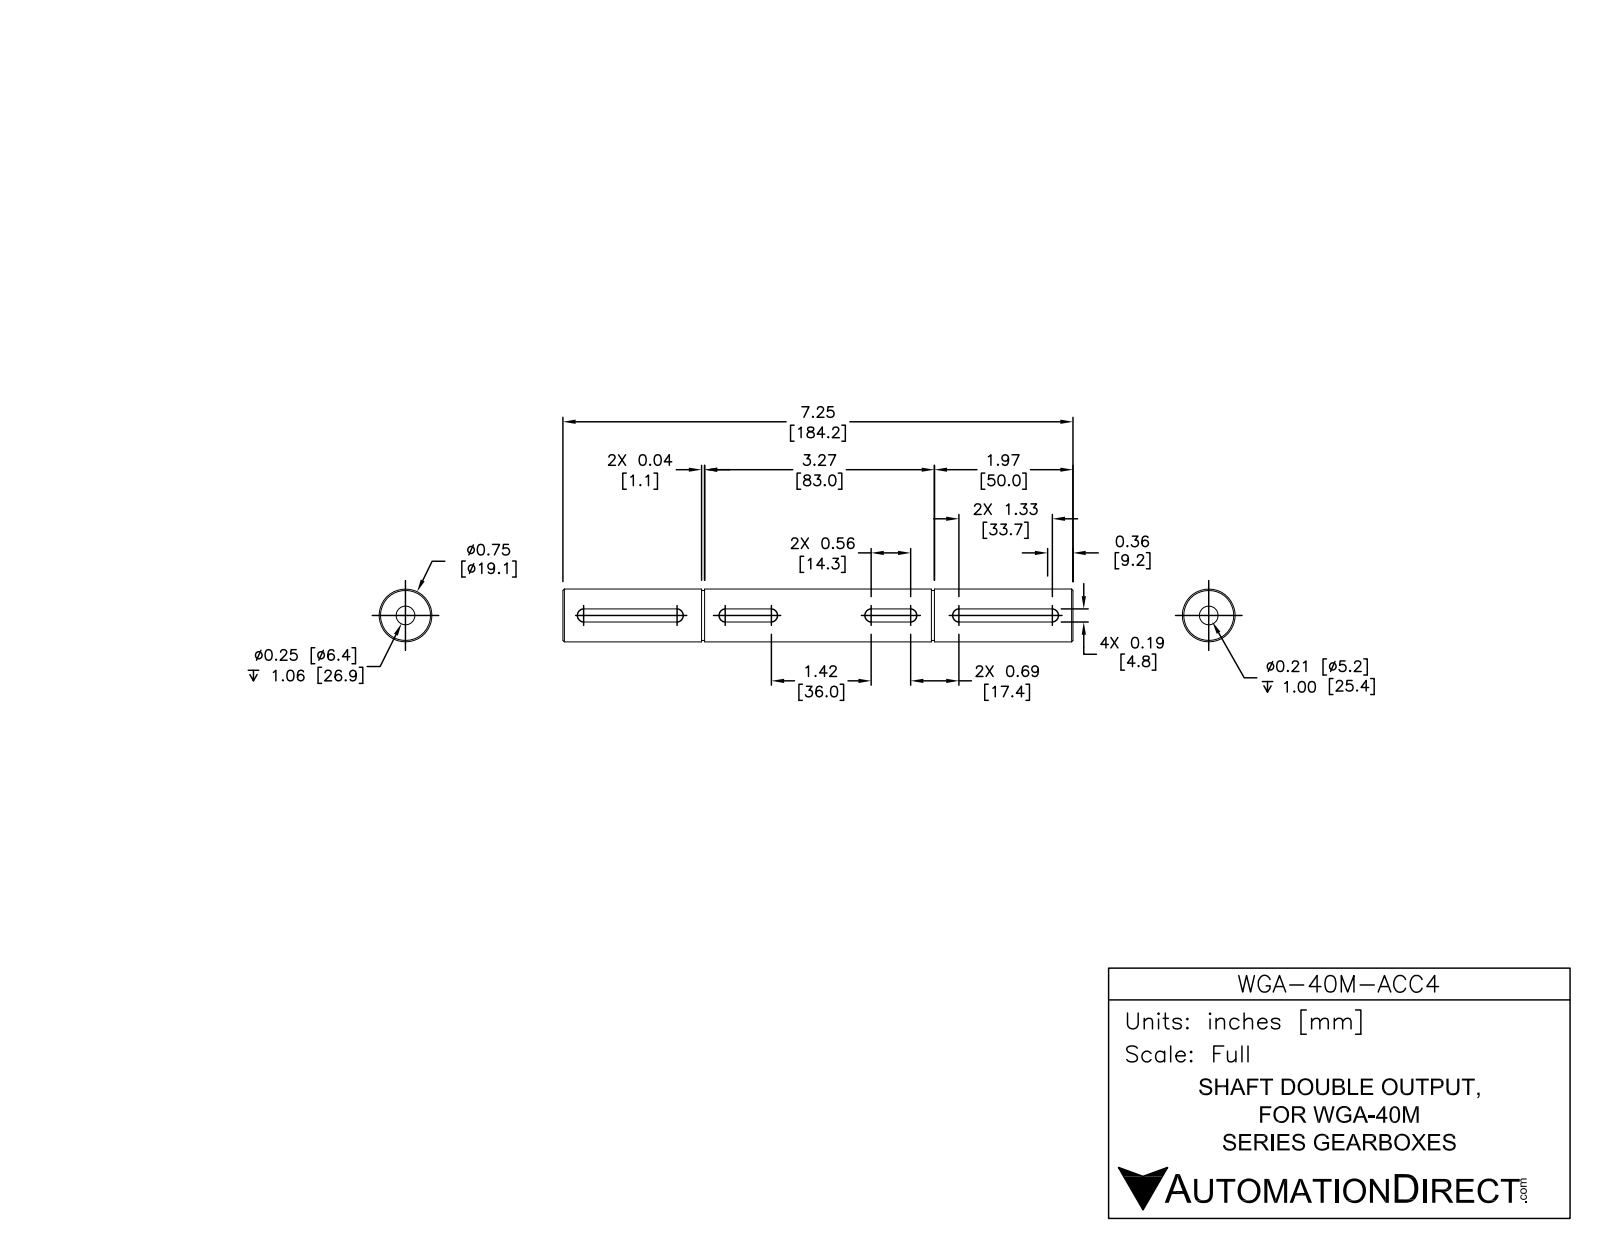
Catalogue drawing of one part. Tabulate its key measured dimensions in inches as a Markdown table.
| quantity | value |
| --- | --- |
| part name | WGA-40M-ACC4 |
| STEP written by | SolidWorks 2014 (AUTOMOTIVE_DESIGN) |
| units | inches |
| bodies | 1 solid, 48 faces (18 planar, 22 cylindrical, 8 other) |
| overall size | 7.25 × 0.75 × 0.75 |
| volume | 3.053 in³ |
| surface area | 19.92 in² |
| round holes (diameter × count) | 0.266 × 1 |
| round bosses / shafts (diameter × count) | 0.75 × 1, 0.709 × 1 |
| partial cylindrical surfaces (radius × count) | 0.094 × 8 |
| main face-to-face distances | 0.187, 7.25, 1.97, 2.013, 5.237, 5.28, 3.267, 0.043, 3.31, 3.223 |
